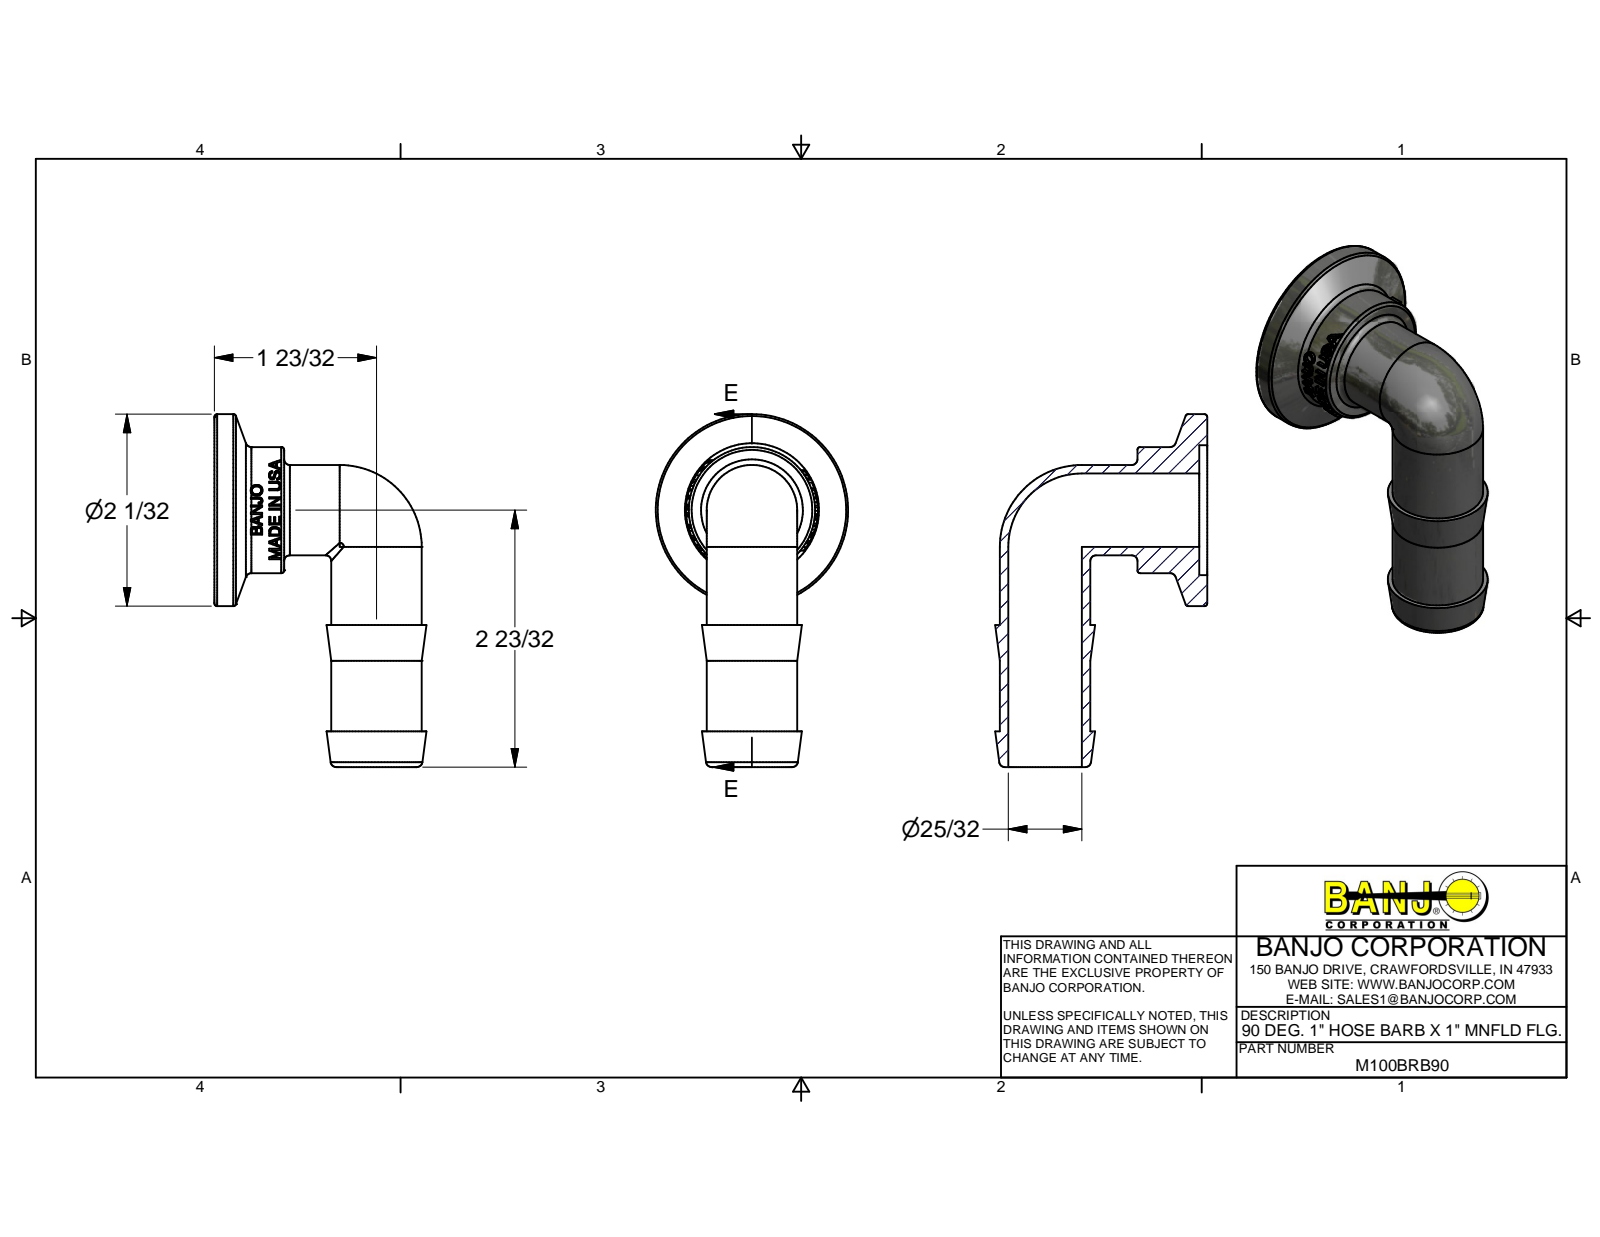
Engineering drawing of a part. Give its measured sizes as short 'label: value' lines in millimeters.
name: M100BRB90
written by: Autodesk Inventor 2012 (AUTOMOTIVE_DESIGN)
unit: mm
bodies: 1 solid, 405 faces (189 planar, 48 cylindrical, 168 other)
size: 95.3 × 57.2 × 51.8
volume: 34 090 mm³; area: 20 060 mm²
holes: 2× ⌀19.8, 1× ⌀35.1
bosses: 2× ⌀24.4, 1× ⌀51.8, 1× ⌀34
rounds: 1× R16.3
face distances: 2.1, 16.7, 18.8, 28.7, 9.7, 38.4, 1.5, 0.4, 4.6, 14.8
